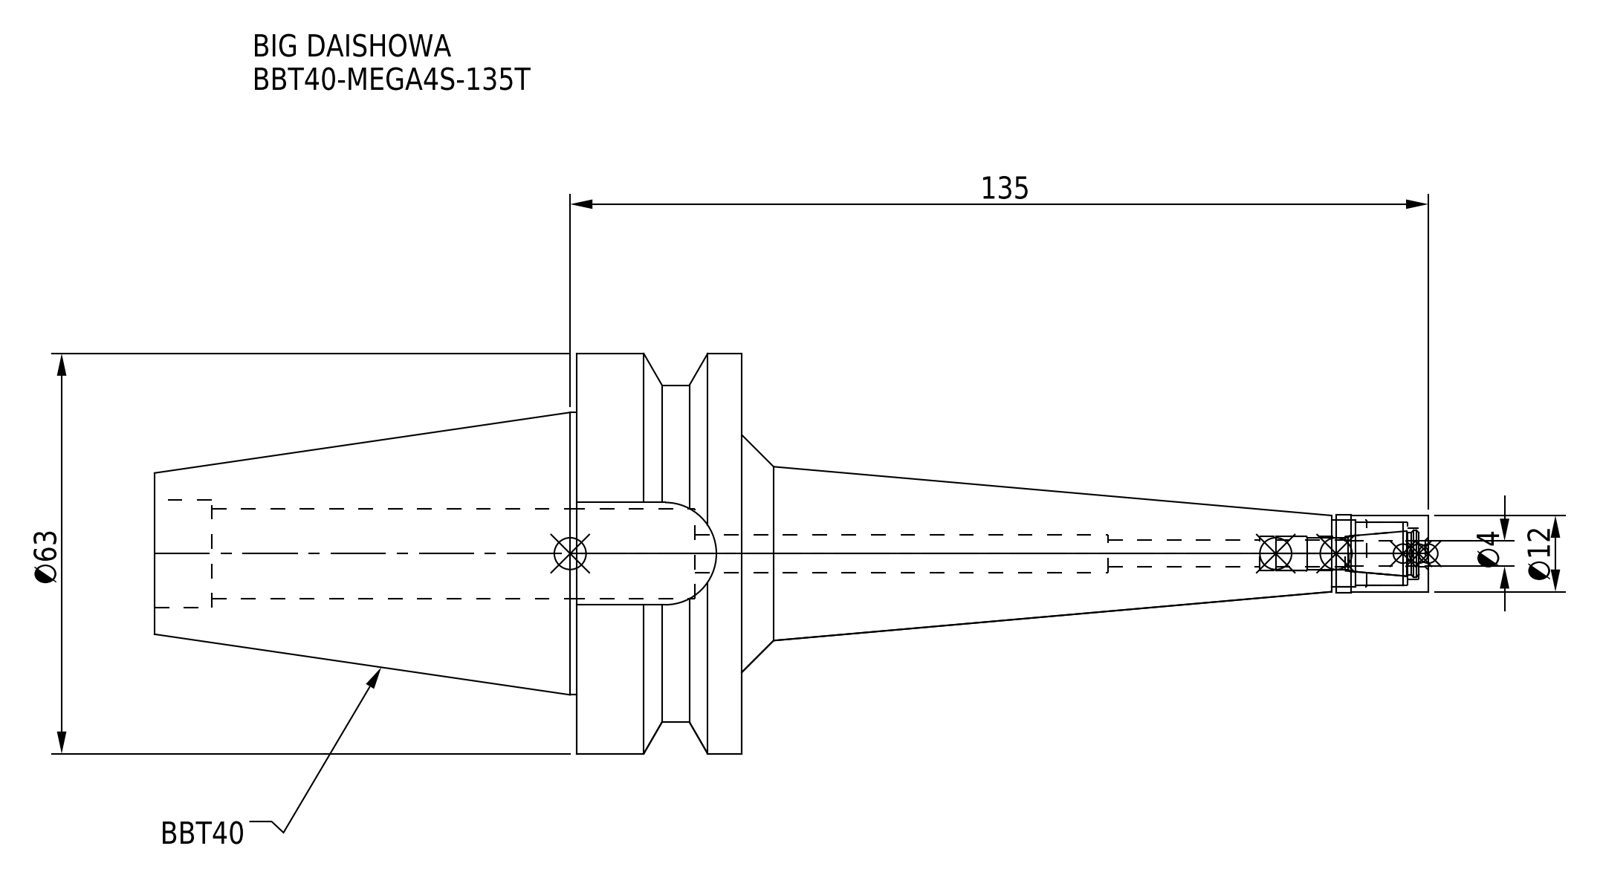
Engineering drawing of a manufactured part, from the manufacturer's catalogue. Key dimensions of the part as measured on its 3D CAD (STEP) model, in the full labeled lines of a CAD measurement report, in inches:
Part name (STEP PRODUCT): BBT40-MEGA4S-135T-040.stp; BBT40-MEGA4S-135T_1.stp; MGN4S_1.stp; DXF_TEMP_ASSY_ASM_4_ASM.stp (+3 more)
STEP written by: SolidWorks 2019 (CONFIG_CONTROL_DESIGN)
Units: inches
Bodies: 2 solids, 74 faces (22 planar, 38 cylindrical, 14 other)
Overall size (bounding box): 7.89 × 2.48 × 2.48
Volume: 9.306 in³ · Surface area: 48.53 in²
Round holes (diameter × count): ⌀0.161 ×1, ⌀0.165 ×1, ⌀0.213 ×1, ⌀0.236 ×1, ⌀0.315 ×1, ⌀0.394 ×1, ⌀0.413 ×1, ⌀0.559 ×1, ⌀0.669 ×1
Round bosses / shafts (diameter × count): ⌀2.48 ×1, ⌀2.087 ×1, ⌀1.75 ×1, ⌀0.484 ×1, ⌀0.472 ×1
Partial cylindrical surfaces — rounded edges, fillets, slot ends (radius × count): R0.317 ×1
Main face-to-face distances: 1.024, 1.772, 3.638, 2.614, 0.634, 0.291, 0.732, 3.346, 4.252, 4.543
